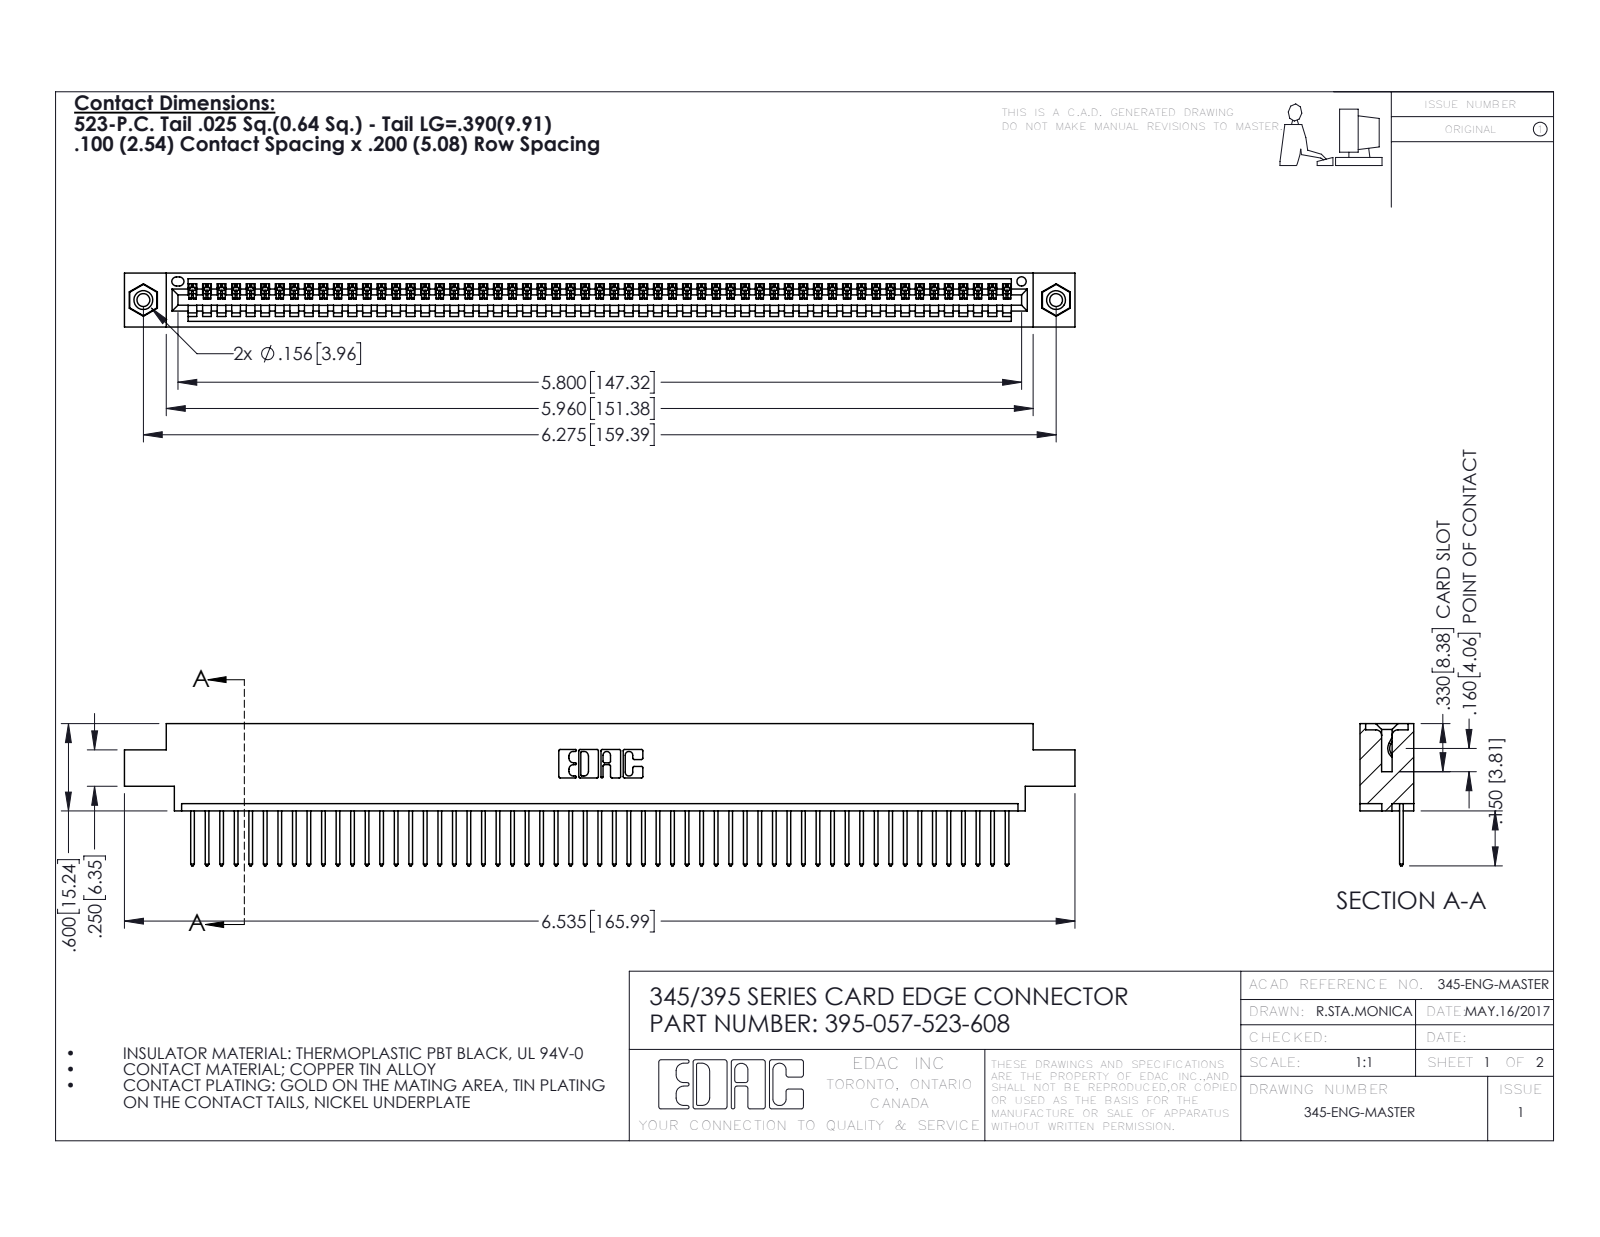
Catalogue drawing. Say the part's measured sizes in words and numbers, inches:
The part is named "345-250-001_345-250-003-102; 345-292-001_345-293-123; 395-057-523-608; 345 Part_0.170 Offset - 0.156 Dia-TI". Its 3-D file was written by "SolidWorks 2016 (CONFIG_CONTROL_DESIGN)". It is 60 solids with 3496 faces: 2396 planar, 1084 cylindrical and 16 other. Overall it measures 6.535 by 0.977 by 0.37 inches. Its volume is 0.961 cubic inches and its surface area 33.07 square inches. Round holes: 2 of diameter 0.089, 2 of diameter 0.125, 2 of diameter 0.156, 1 of diameter 0.064. Round bosses or shafts: 2 of diameter 0.155. Partial cylindrical surfaces (rounded edges, fillets, slot ends): 114 of radius 0.006, 114 of radius 0.01, 22 of radius 0.01, 6 of radius 0.007, 6 of radius 0.031, 3 of radius 0.026, 2 of radius 0.031, 2 of radius 0.04. The main face-to-face distances are 0.072, 0.298, 0.37, 0.098, 0.272, 0.025, 0.2, 0.225, 0.175, 0.149. The hole center spacings are 0.27, 6.039, 6.275.
